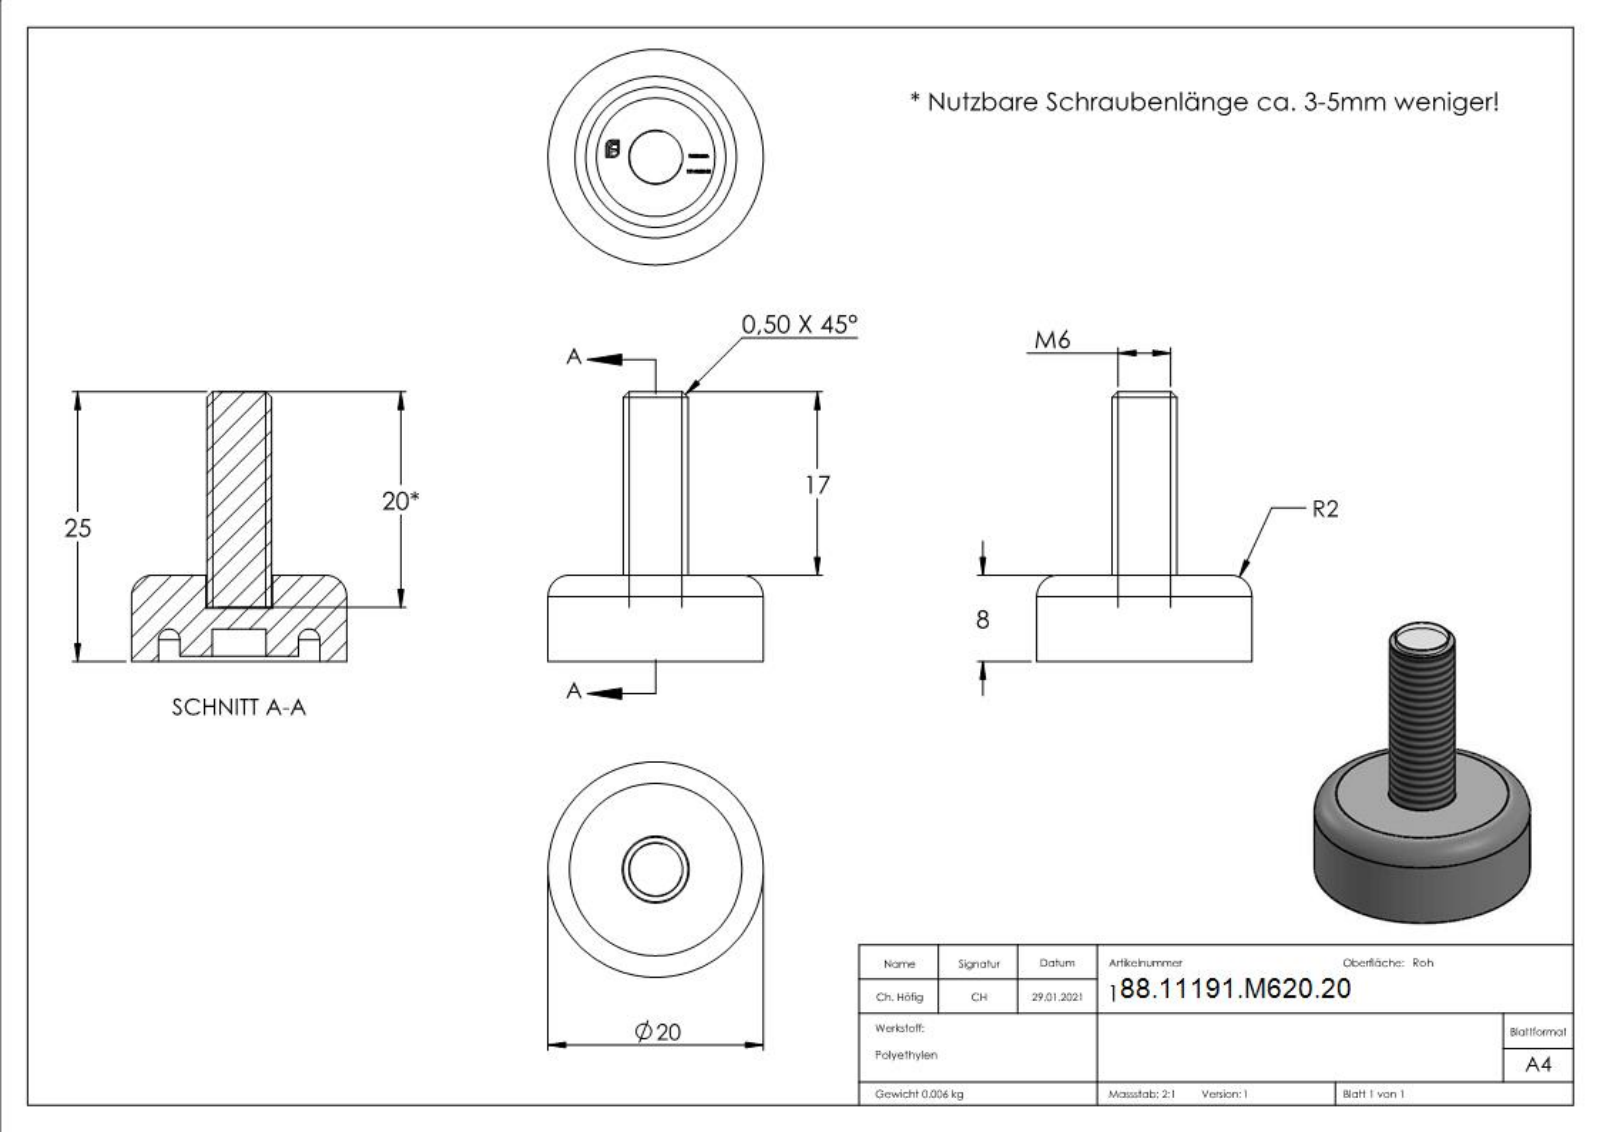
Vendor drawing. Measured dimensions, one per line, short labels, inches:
name: 191-M620-20
written by: SolidWorks 2018 (CONFIG_CONTROL_DESIGN)
unit: in
bodies: 2 solids, 295 faces (159 planar, 12 cylindrical, 124 other)
size: 0.984 × 0.787 × 0.787
volume: 0.159 in³; area: 2.788 in²
holes: 1× ⌀0.197, 1× ⌀0.244, 1× ⌀0.591
bosses: 1× ⌀0.787, 1× ⌀0.433, 1× ⌀0.236
face distances: 0.315, 0.295, 0.02, 0.118, 0.197, 0.173, 0.193, 0.122, 0.177, 0.098
